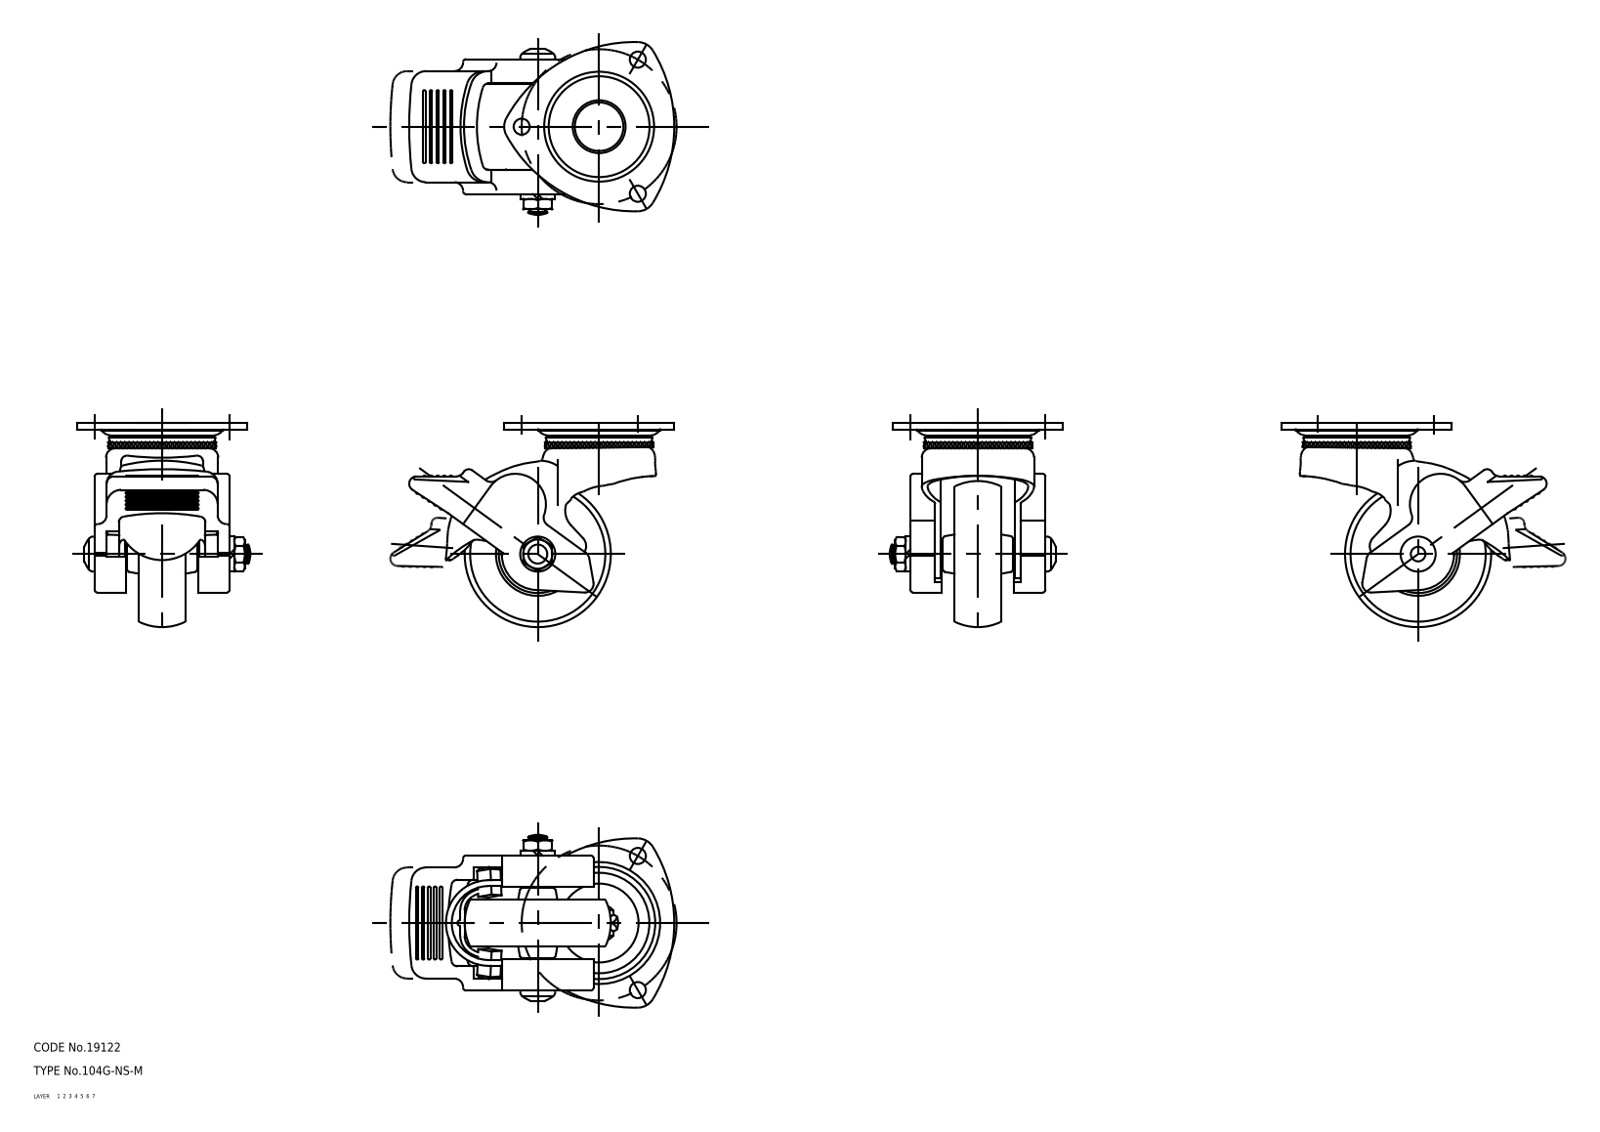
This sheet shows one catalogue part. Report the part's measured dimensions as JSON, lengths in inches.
{"part_name": "lever; wheel; mounting plate; main shaft (+2 more)", "step_written_by": "CADfix (AUTOMOTIVE_DESIGN)", "units": "inches", "bodies": {"solids": 6, "faces": 441, "planar": 0, "cylindrical": 0, "other": 441}, "overall_size": [3.57, 2.756, 2.329], "volume_in3": 4.665, "surface_area_in2": 58.99}
